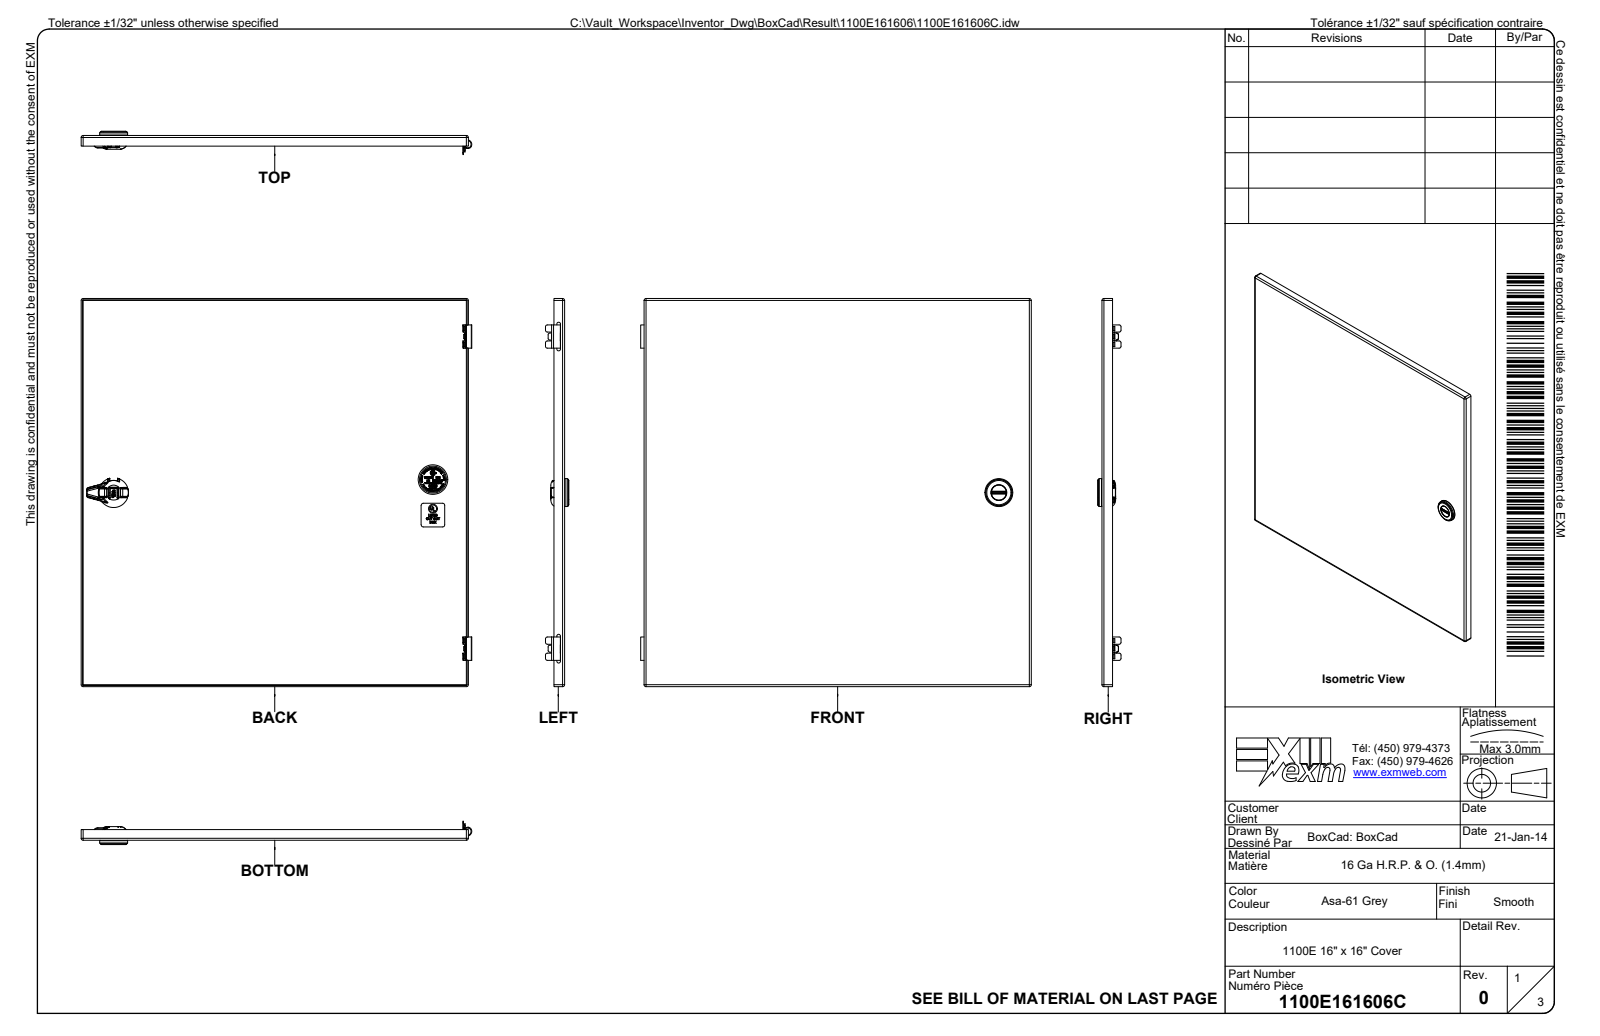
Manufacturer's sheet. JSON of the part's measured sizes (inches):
{"part_name": "1100E161606; 1100E161606B; 1100E161606B-P; 1100E161606C (+8 more)", "step_written_by": "Autodesk Inventor 2024 (AUTOMOTIVE_DESIGN)", "units": "inches", "bodies": {"solids": 8, "faces": 4017, "planar": 2166, "cylindrical": 760, "other": 1091}, "overall_size": [16.544, 16.4, 6.249], "volume_in3": 52.96, "surface_area_in2": 1980, "round_holes": [[1.125, 12], [0.875, 8], [1.375, 6], [0.29, 4], [0.177, 2], [1.75, 2], [0.03, 1], [0.043, 1], [0.375, 1], [1.063, 1]], "round_bosses_or_shafts": [[1.125, 12], [0.875, 8], [1.375, 6], [1.75, 2], [1.26, 1], [1.25, 1], [1.181, 1], [1.142, 1]], "partial_cylinders_radius": [[0.01, 219], [0.031, 22], [0.02, 19], [0.079, 18], [0.086, 14], [0.084, 8], [0.009, 7], [0.039, 4]], "face_to_face_distances": [0.055, 15.945, 0.053, 6.015, 6.068, 5.96, 6.013, 16, 15.89, 5.945], "hole_center_spacings": [1.693, 7.126, 1.901, 3.376, 3.568, 5.261, 5.439, 8.815]}
